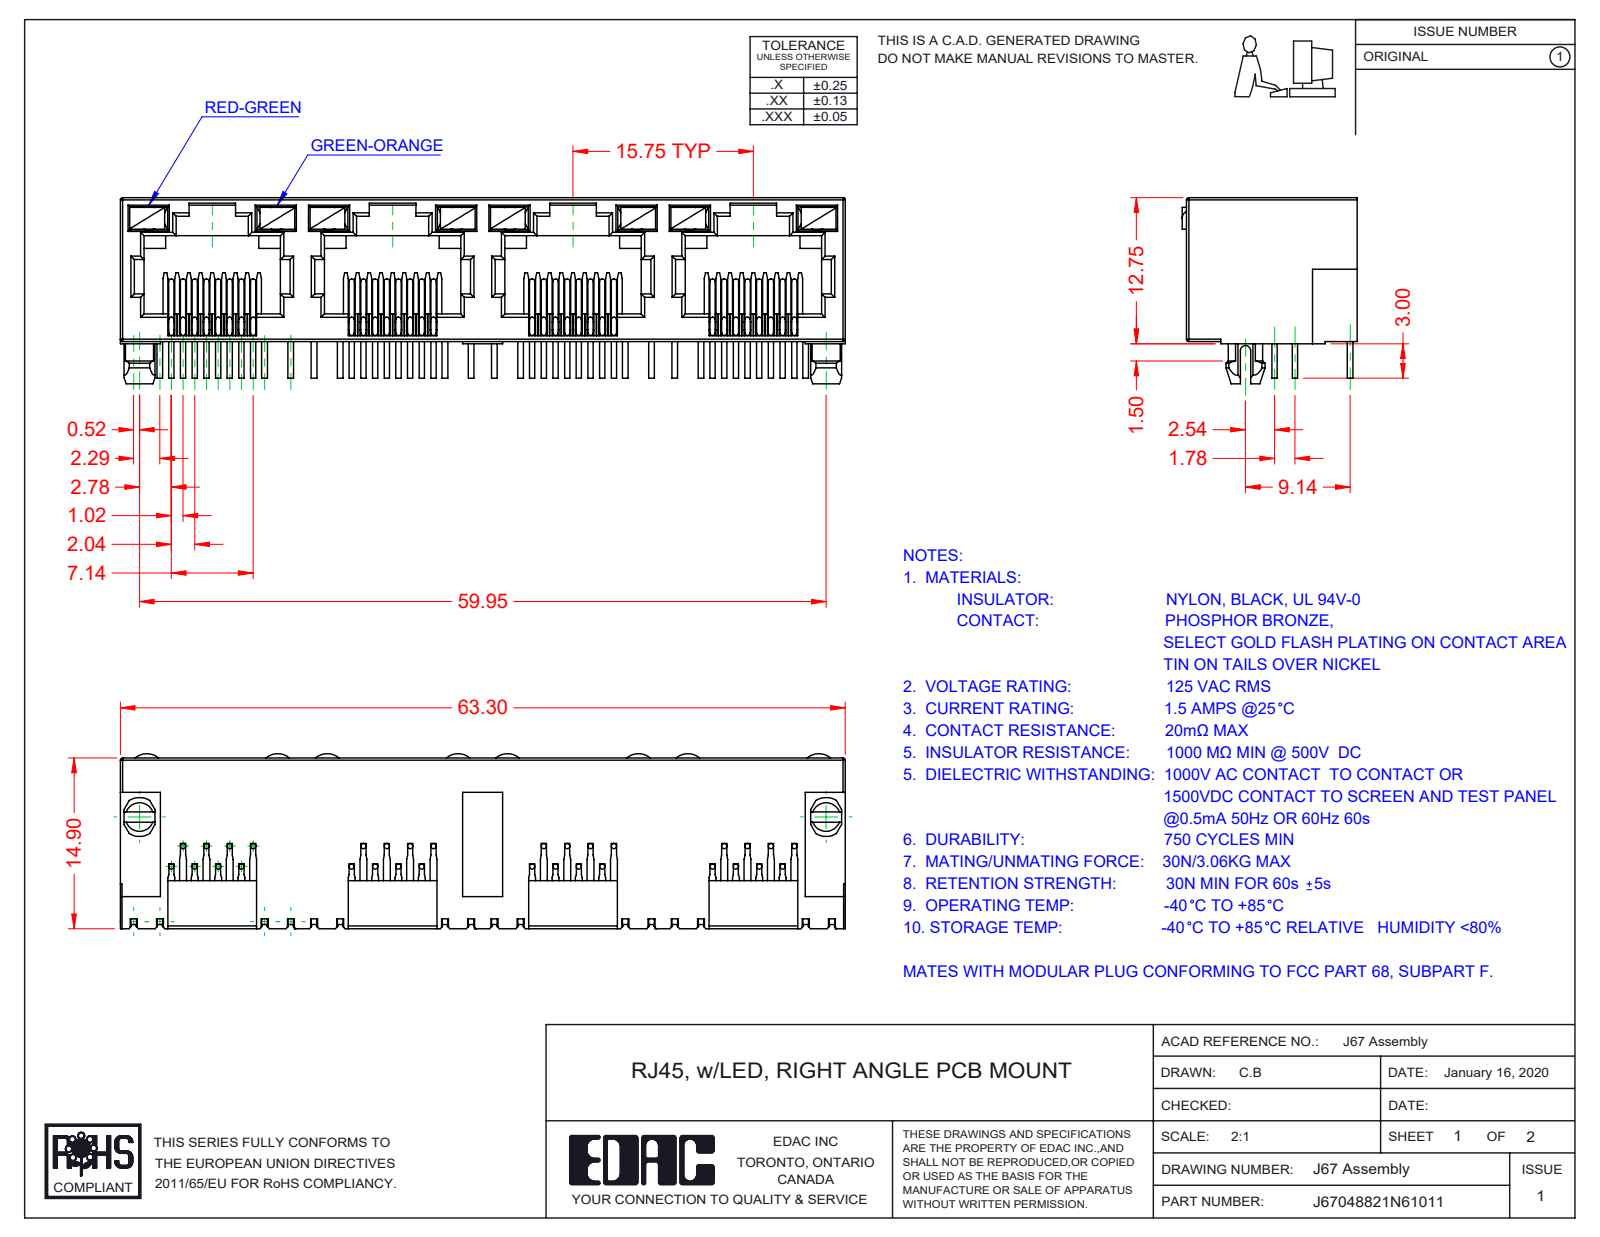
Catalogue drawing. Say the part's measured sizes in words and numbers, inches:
The part is named "J67048822N67011; 67 LED RH_7-Green-Orange; 67 LED LH_6-Red-Green; 67 Contacts (+1 more)". Its 3-D file was written by "SolidWorks 2016 (CONFIG_CONTROL_DESIGN)". It is 41 solids with 2481 faces: 1781 planar, 492 cylindrical and 208 other. Overall it measures 2.492 by 0.64 by 0.602 inches. Its volume is 0.315 cubic inches and its surface area 17.94 square inches. Round bosses or shafts: 96 of diameter 0.018. Partial cylindrical surfaces (rounded edges, fillets, slot ends): 66 of radius 0.008, 29 of radius 0.012, 9 of radius 0.018, 8 of radius 0.061, 2 of radius 0.059, 2 of radius 0.067, 1 of radius 0.014, 1 of radius 0.039. The main face-to-face distances are 0.02, 0.494, 0.074, 0.035, 0.394, 0.62, 0.039, 0.055, 0.433, 0.468.
